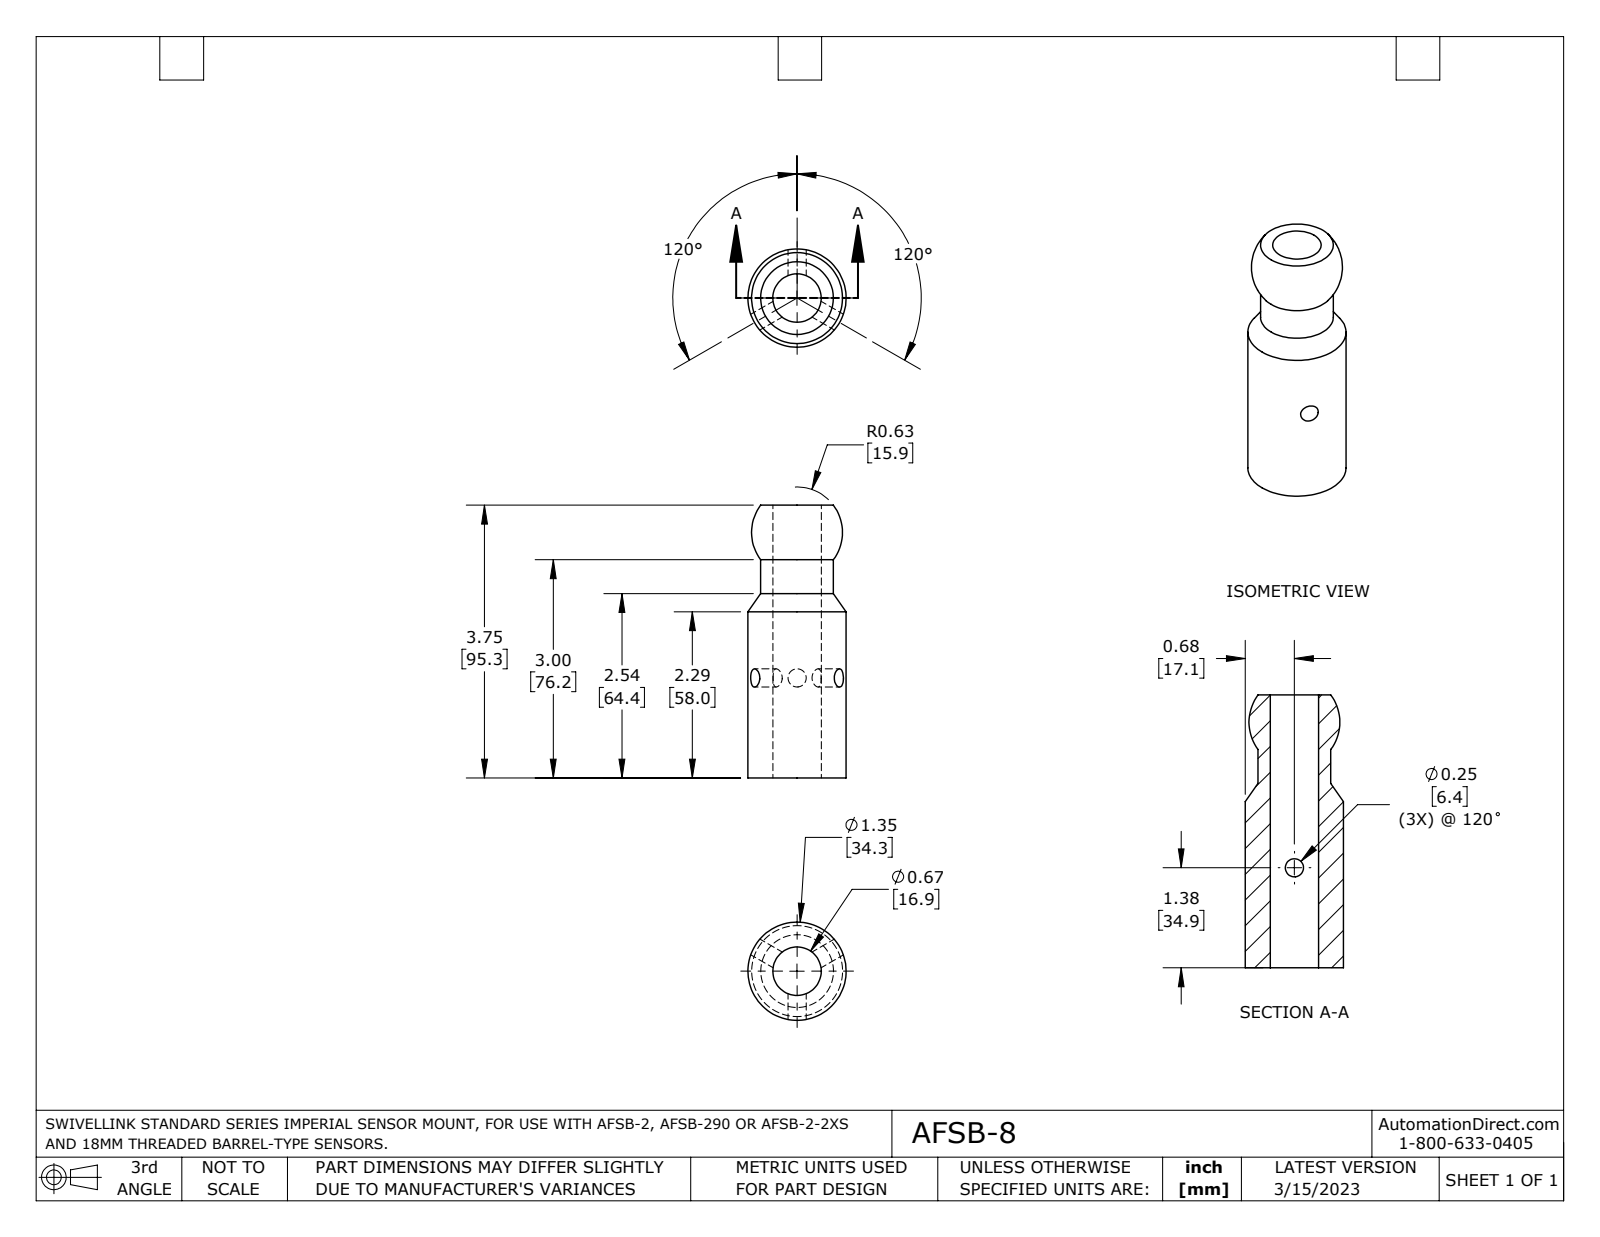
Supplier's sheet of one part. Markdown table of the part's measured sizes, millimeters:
| quantity | value |
| --- | --- |
| part name | AFSB-8 |
| STEP written by | SolidWorks 2021 (AUTOMOTIVE_DESIGN) |
| units | millimeters |
| bodies | 1 solid, 11 faces (2 planar, 6 cylindrical, 3 other) |
| overall size | 101.6 × 34.3 × 34.3 |
| volume | 38 330 mm³ |
| surface area | 15 570 mm² |
| round holes (diameter × count) | 6.4 × 3, 16.9 × 1 |
| round bosses / shafts (diameter × count) | 34.3 × 1, 25.4 × 1 |
| main face-to-face distances | 95.3 |
